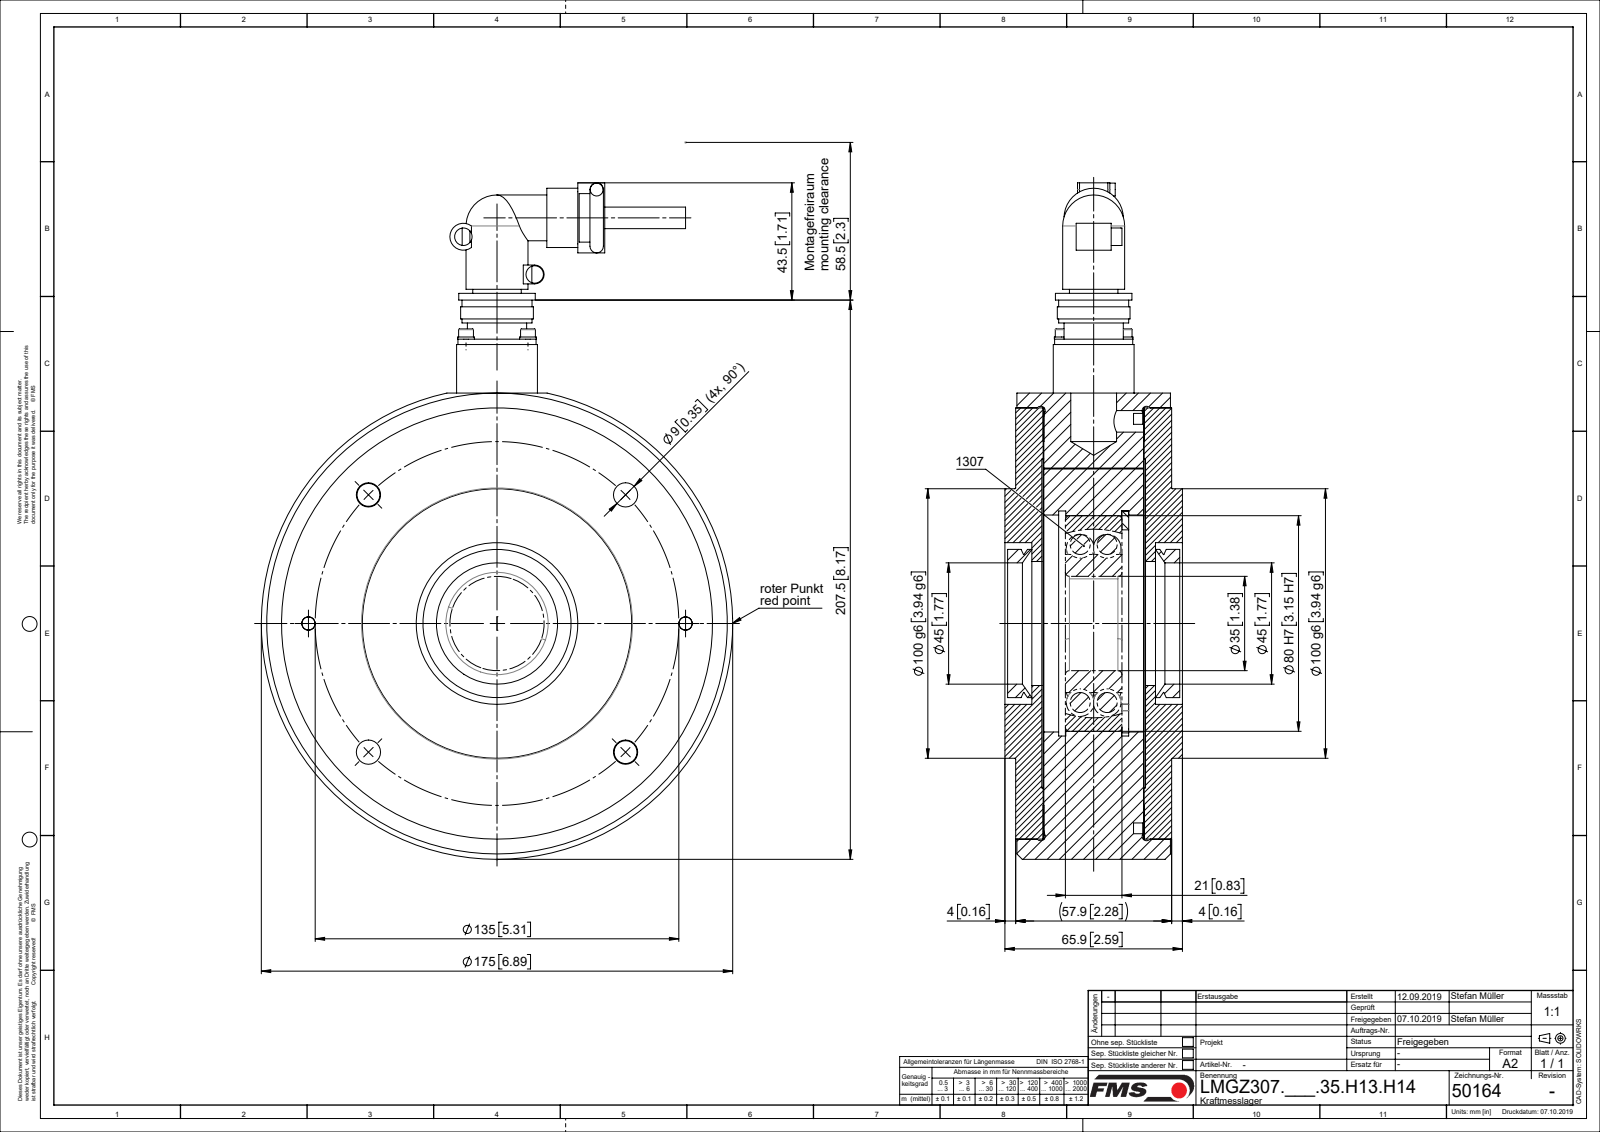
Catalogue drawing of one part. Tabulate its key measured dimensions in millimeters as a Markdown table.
| quantity | value |
| --- | --- |
| part name | L50164; L4857104; TEIL1; L47388 (+8 more) |
| STEP written by | Mechanical Desktop 2007 (CONFIG_CONTROL_DESIGN) |
| units | millimeters |
| bodies | 21 solids, 403 faces (111 planar, 233 cylindrical, 59 other) |
| overall size | 251 × 175 × 65.9 |
| volume | 1 300 000 mm³ |
| surface area | 270 492 mm² |
| round holes (diameter × count) | 2.6 × 4, 3.2 × 4, 3.4 × 4, 3.5 × 4, 9 × 4, 5 × 2, 6.6 × 2, 11 × 2, 23 × 1, 35 × 1, 44 × 1, 46 × 1 |
| round bosses / shafts (diameter × count) | 6.2 × 4, 5.5 × 4, 3 × 4, 22 × 2, 10 × 2, 6.5 × 2, 6 × 2, 4.8 × 2 |
| partial cylindrical surfaces (radius × count) | 2.5 × 2, 7.5 × 2, 3.5 × 1, 5 × 1 |
| main face-to-face distances | 37.25, 10.2, 10.45, 47.45, 47.7, 37, 0.5, 38, 9.7, 48.2 |
| hole center spacings | 16.26, 23, 52.67, 67.5, 95.46, 127.04, 32.53, 70 |
